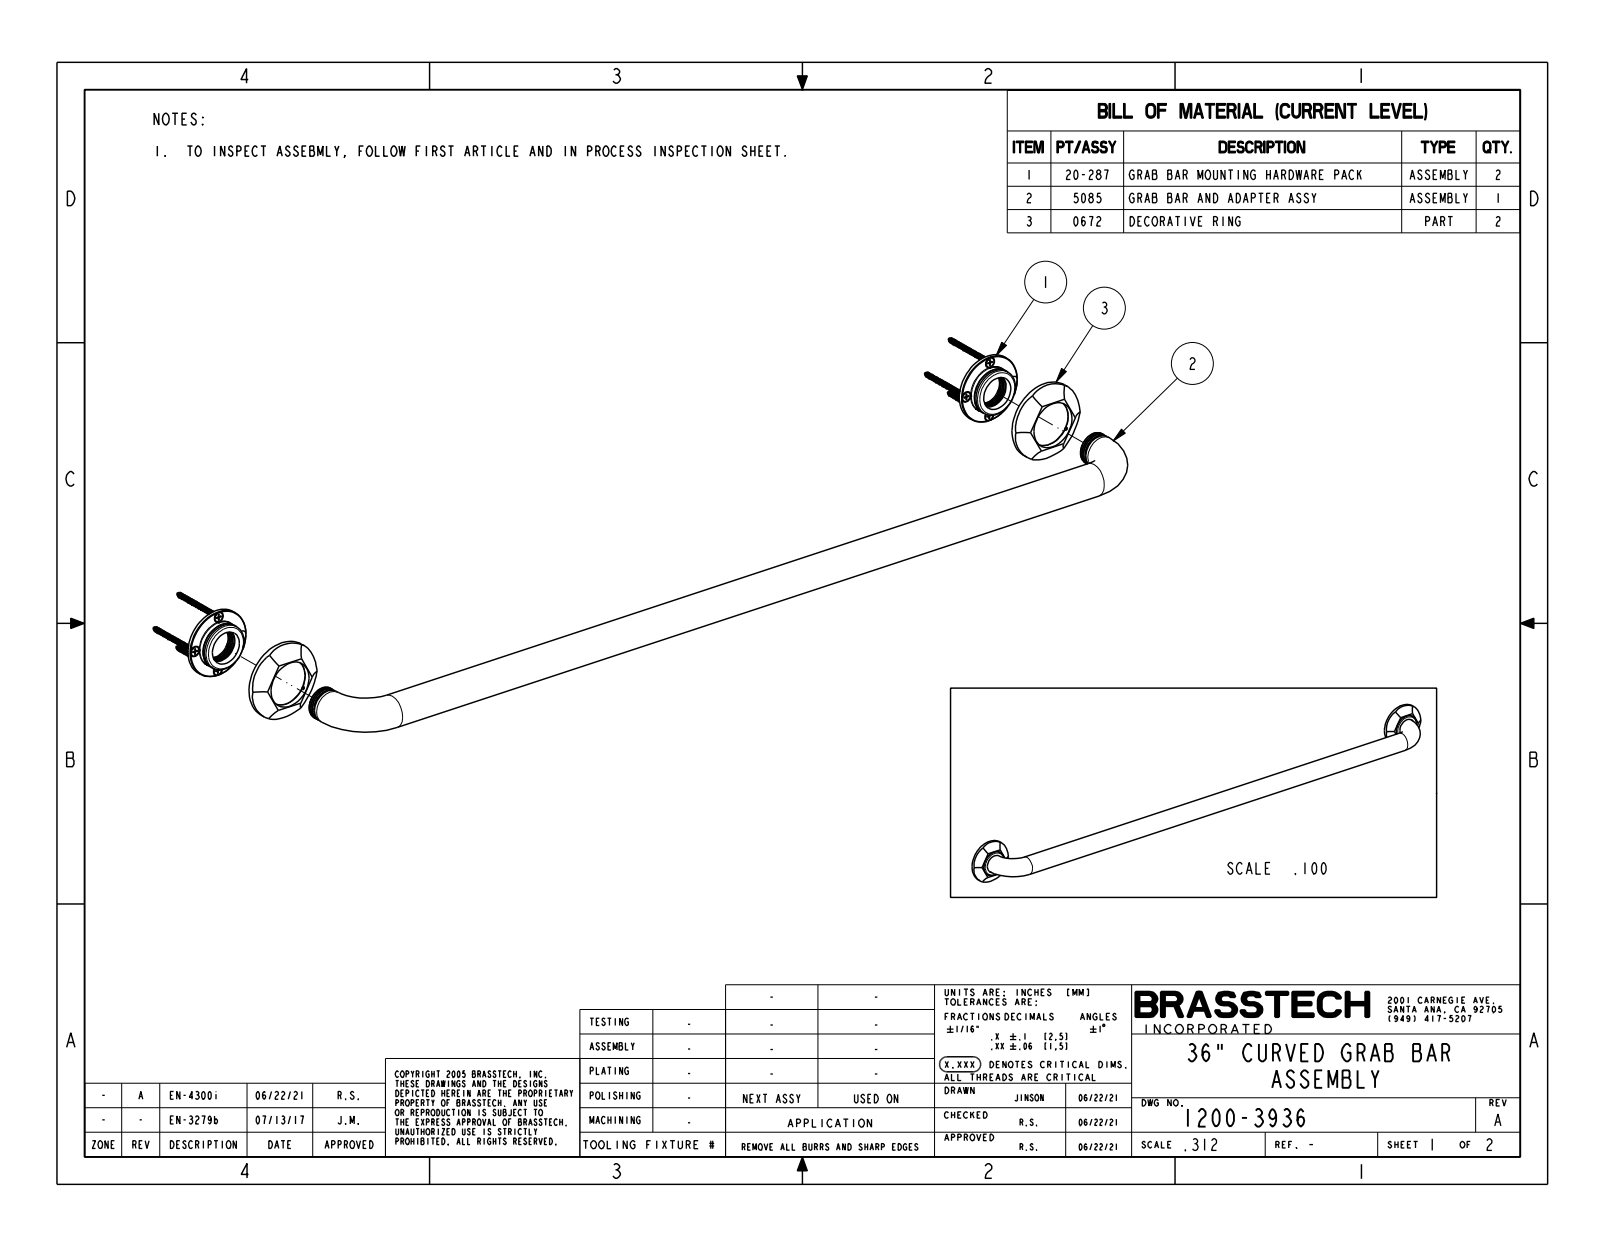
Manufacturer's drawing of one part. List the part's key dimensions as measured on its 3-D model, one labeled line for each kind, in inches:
Part name (STEP PRODUCT): 1200-3936_SW0001
STEP written by: CREO PARAMETRIC BY PTC INC, 2018400 (CONFIG_CONTROL_DESIGN)
Units: inches
Bodies: 1 solid, 36 faces (6 planar, 22 cylindrical, 8 other)
Overall size (bounding box): 39 × 3 × 2.75
Volume: 52.1 in³ · Surface area: 179.2 in²
Round bosses / shafts (diameter × count): ⌀3 ×2, ⌀1.75 ×2, ⌀1.25 ×1
Partial cylindrical surfaces — rounded edges, fillets, slot ends (radius × count): R1.181 ×10
Main face-to-face distances: 0.6, 0.525, 0.075
